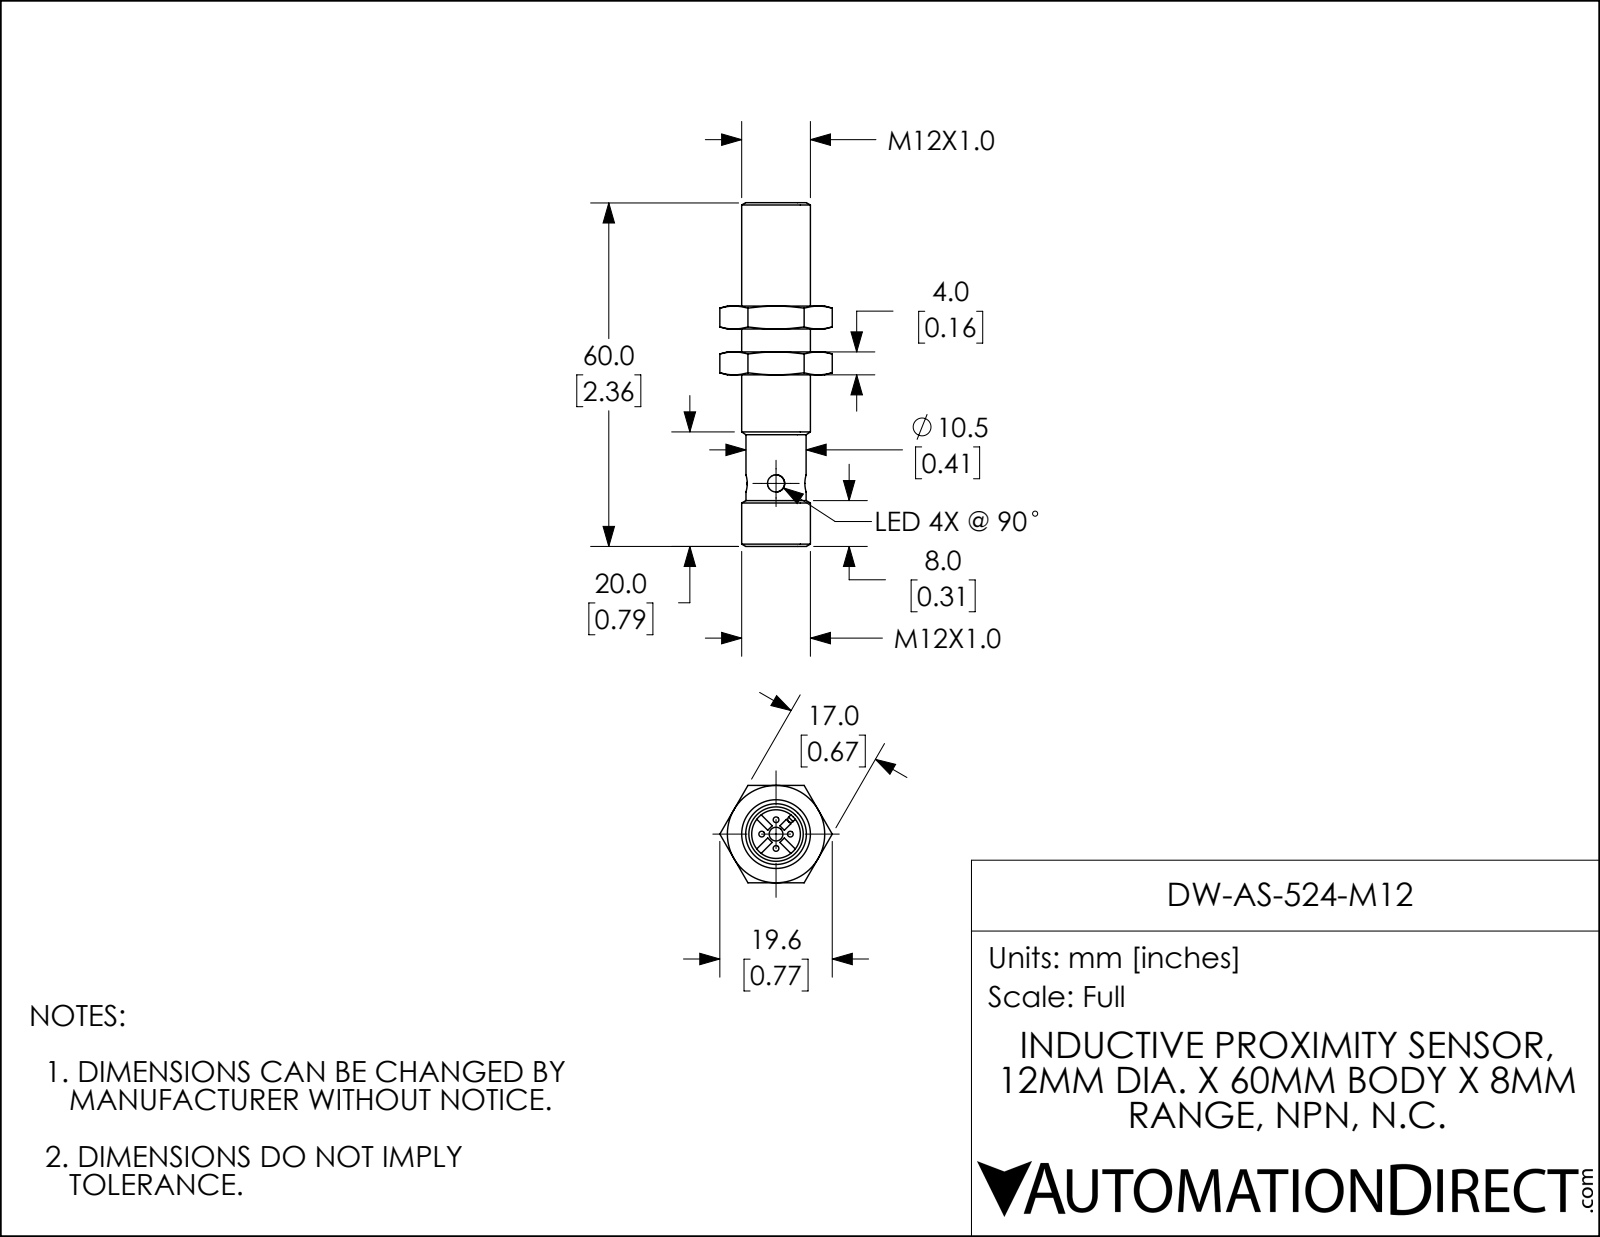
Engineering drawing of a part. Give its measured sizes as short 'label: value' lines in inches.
name: DW-AS-524-M12
written by: SolidWorks 2018 (AUTOMOTIVE_DESIGN)
unit: in
bodies: 3 solids, 104 faces (46 planar, 19 cylindrical, 39 other)
size: 2.362 × 0.773 × 0.669
volume: 0.439 in³; area: 6.386 in²
holes: 2× ⌀0.118, 1× ⌀0.094, 1× ⌀0.335, 1× ⌀0.415, 1× ⌀0.43
bosses: 4× ⌀0.039, 1× ⌀0.472, 1× ⌀0.413, 1× ⌀0.406
rounds: 2× R0.022
face distances: 0.157, 0.315, 0.669, 0.472, 1.183, 1.026, 0.868, 0.711, 0.837, 0.994
